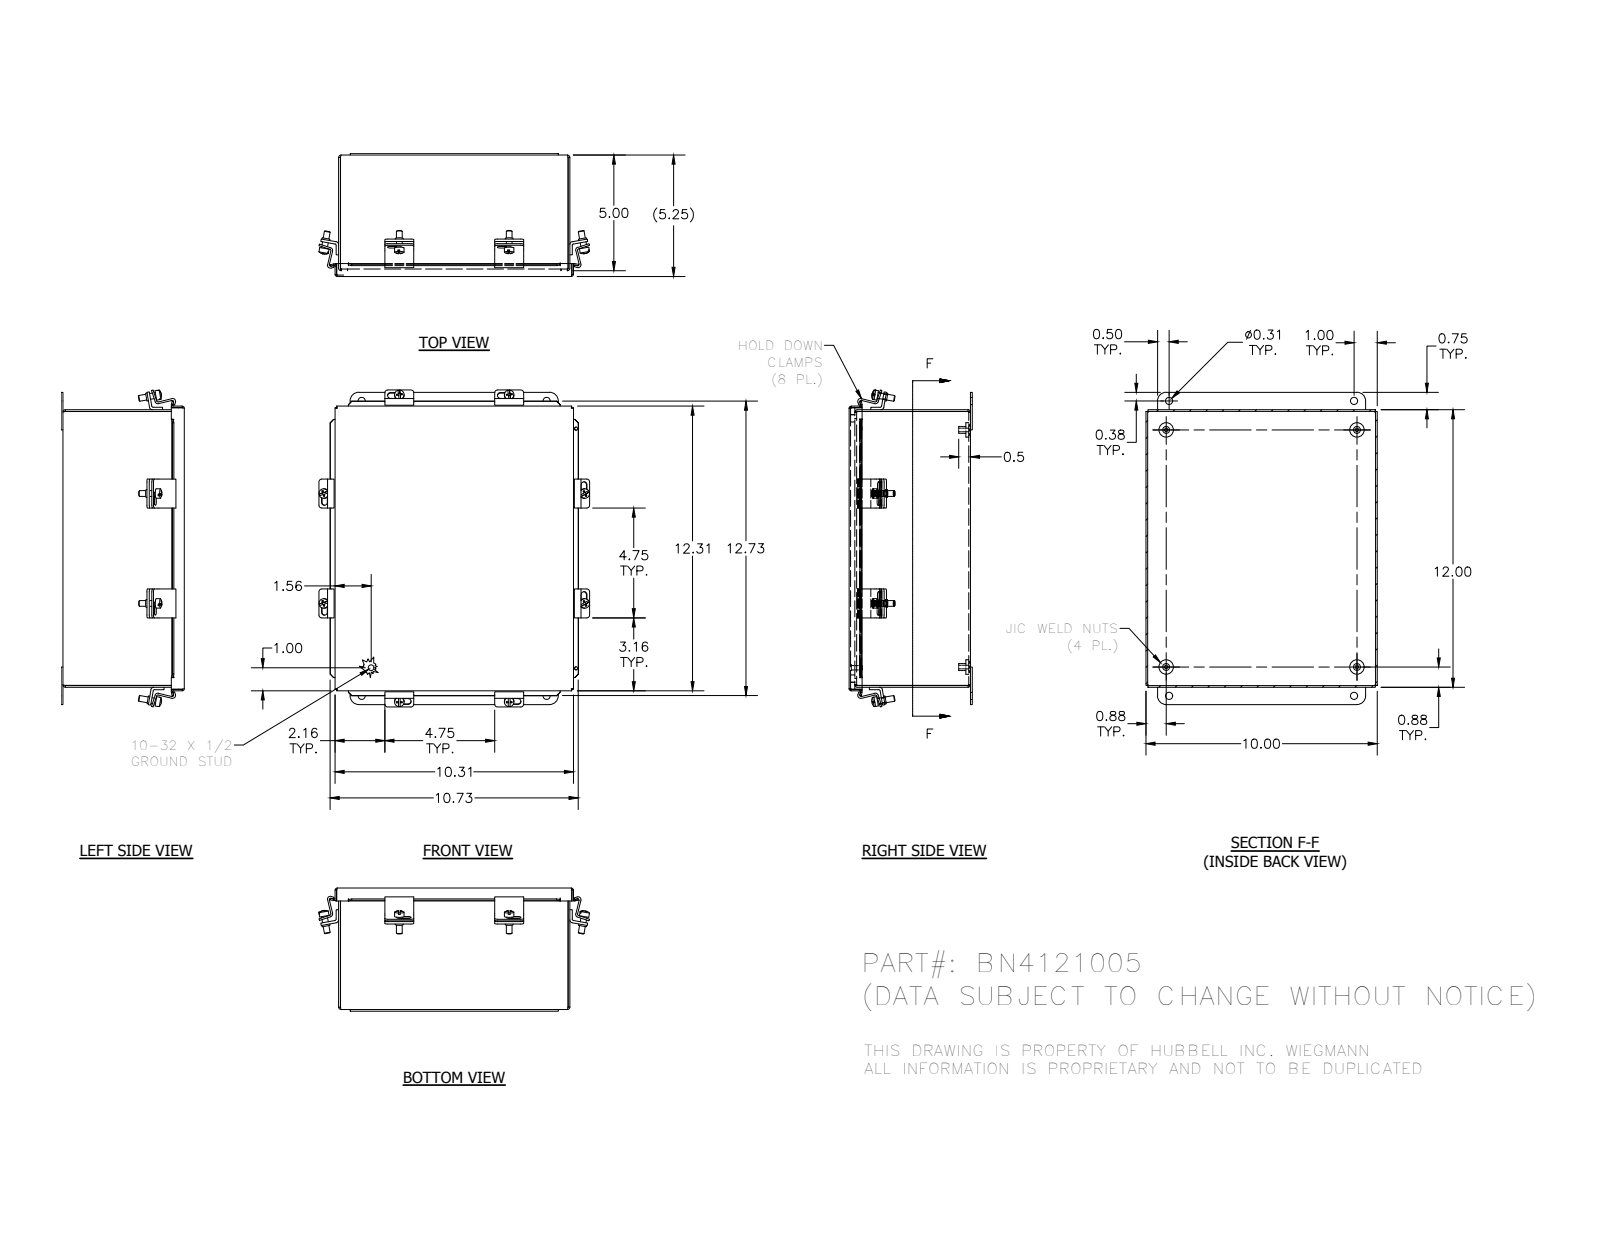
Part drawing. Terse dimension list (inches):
name: BN4121005BKP_1; C1001_1; 3484_1; 3499_1 (+6 more)
written by: SolidWorks 2014 (AUTOMOTIVE_DESIGN)
unit: in
bodies: 35 solids, 785 faces (431 planar, 268 cylindrical, 86 other)
size: 13.704 × 11.705 × 5.324
volume: 45.25 in³; area: 1 215 in²
holes: 8× ⌀0.196, 4× ⌀0.156, 4× ⌀0.31, 2× ⌀0.136
bosses: 9× ⌀0.25, 8× ⌀0.41, 8× ⌀0.344, 4× ⌀0.625, 4× ⌀0.3, 1× ⌀0.19
rounds: 32× R0.125, 16× R0.031, 16× R0.133, 12× R0.063, 12× R0.126, 8× R0.093, 8× R0.105, 4× R0.375
face distances: 0.074, 5.187, 0.062, 5.25, 5.113, 5.176, 9.926, 11.926, 10, 9.852
hole spacings: 1.256, 4.75, 11.501, 14.081, 8, 8.22, 8.221, 8.25
